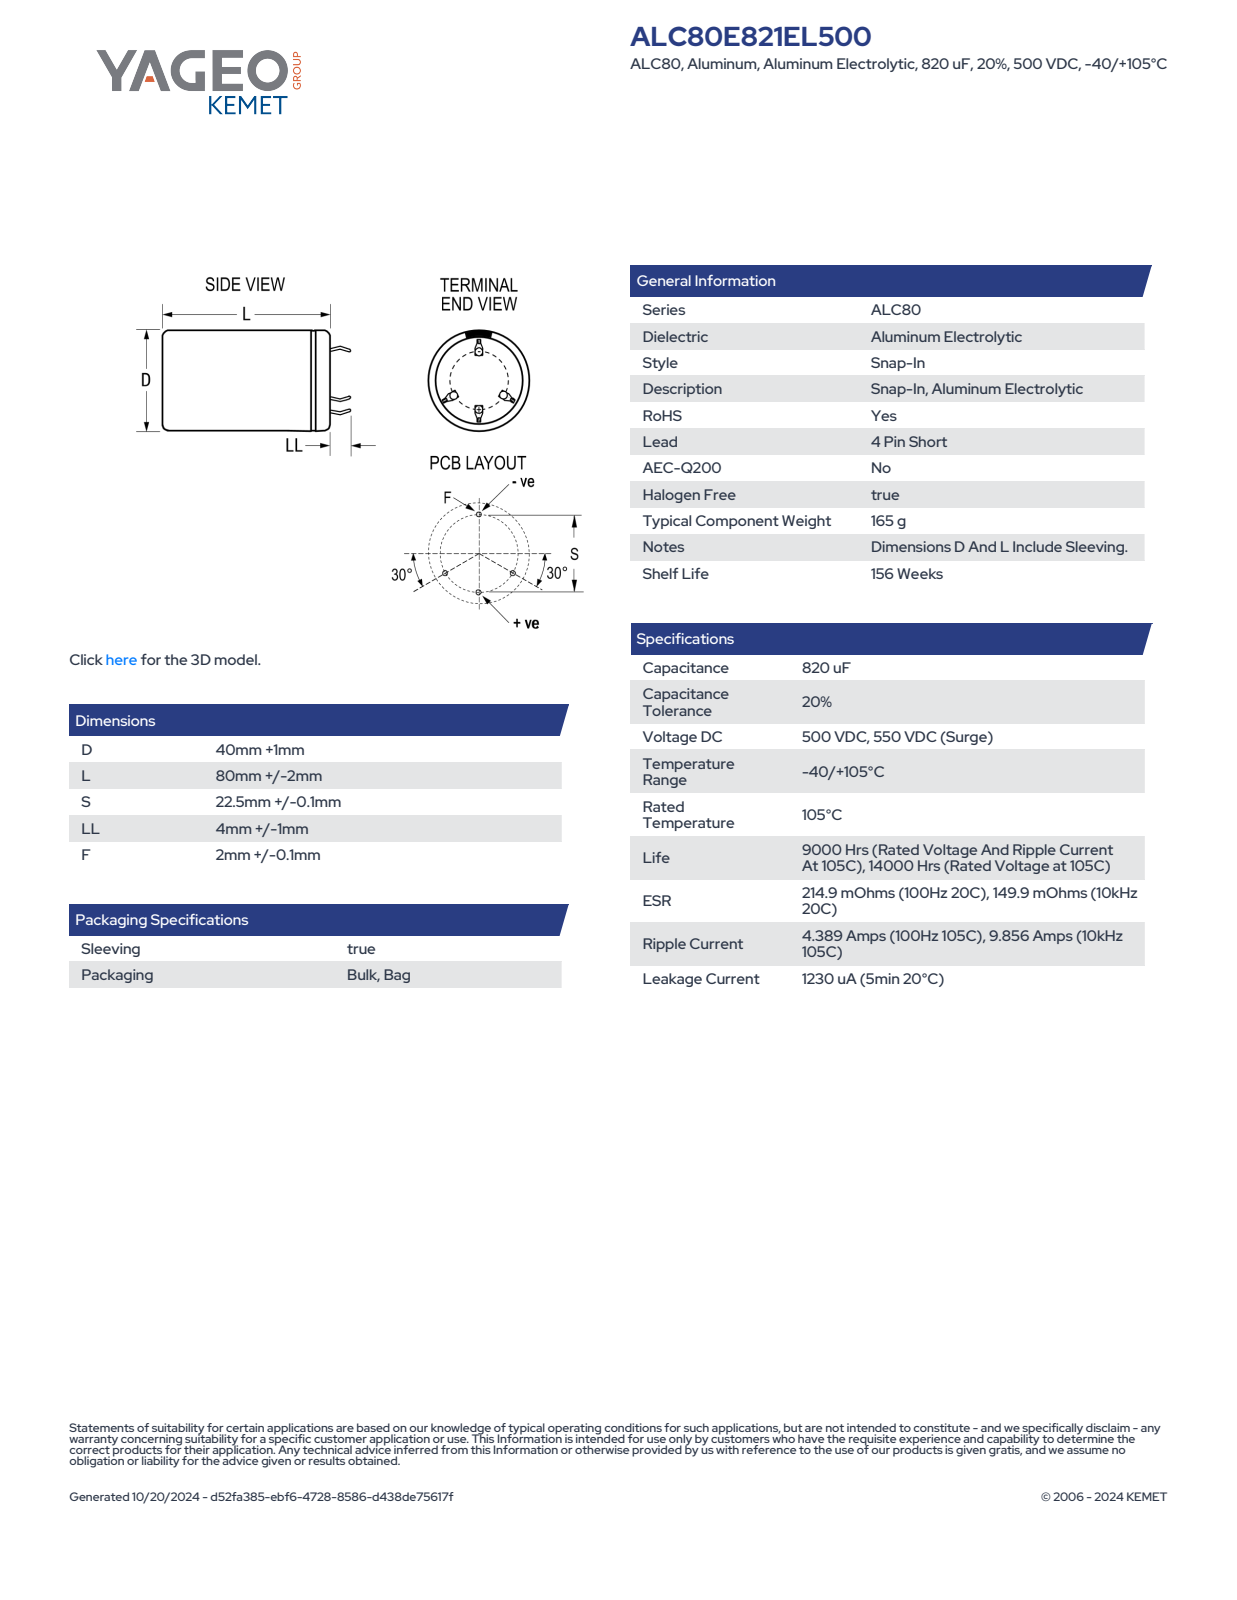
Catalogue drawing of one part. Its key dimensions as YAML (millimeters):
part_name: "CARS_K4P_40X80_D41L82S22.5LL5F2.1"
step_written_by: "SolidWorks 2014 (AUTOMOTIVE_DESIGN)"
units: millimeters
bodies: {solids: 1, faces: 134, planar: 80, cylindrical: 15, other: 39}
overall_size: [86.99, 41, 41]
volume: 107486
surface_area: 13235
round_holes:
  - {diameter: 36.28, count: 1}
round_bosses_or_shafts:
  - {diameter: 41, count: 1}
partial_cylinders:
  - {radius: 20.49, count: 1}
face_to_face_distances: [81.99, 82.49, 0.5, 14.06, 0.6, 0.75, 1.35, 14.33, 13.79, 2.1]
